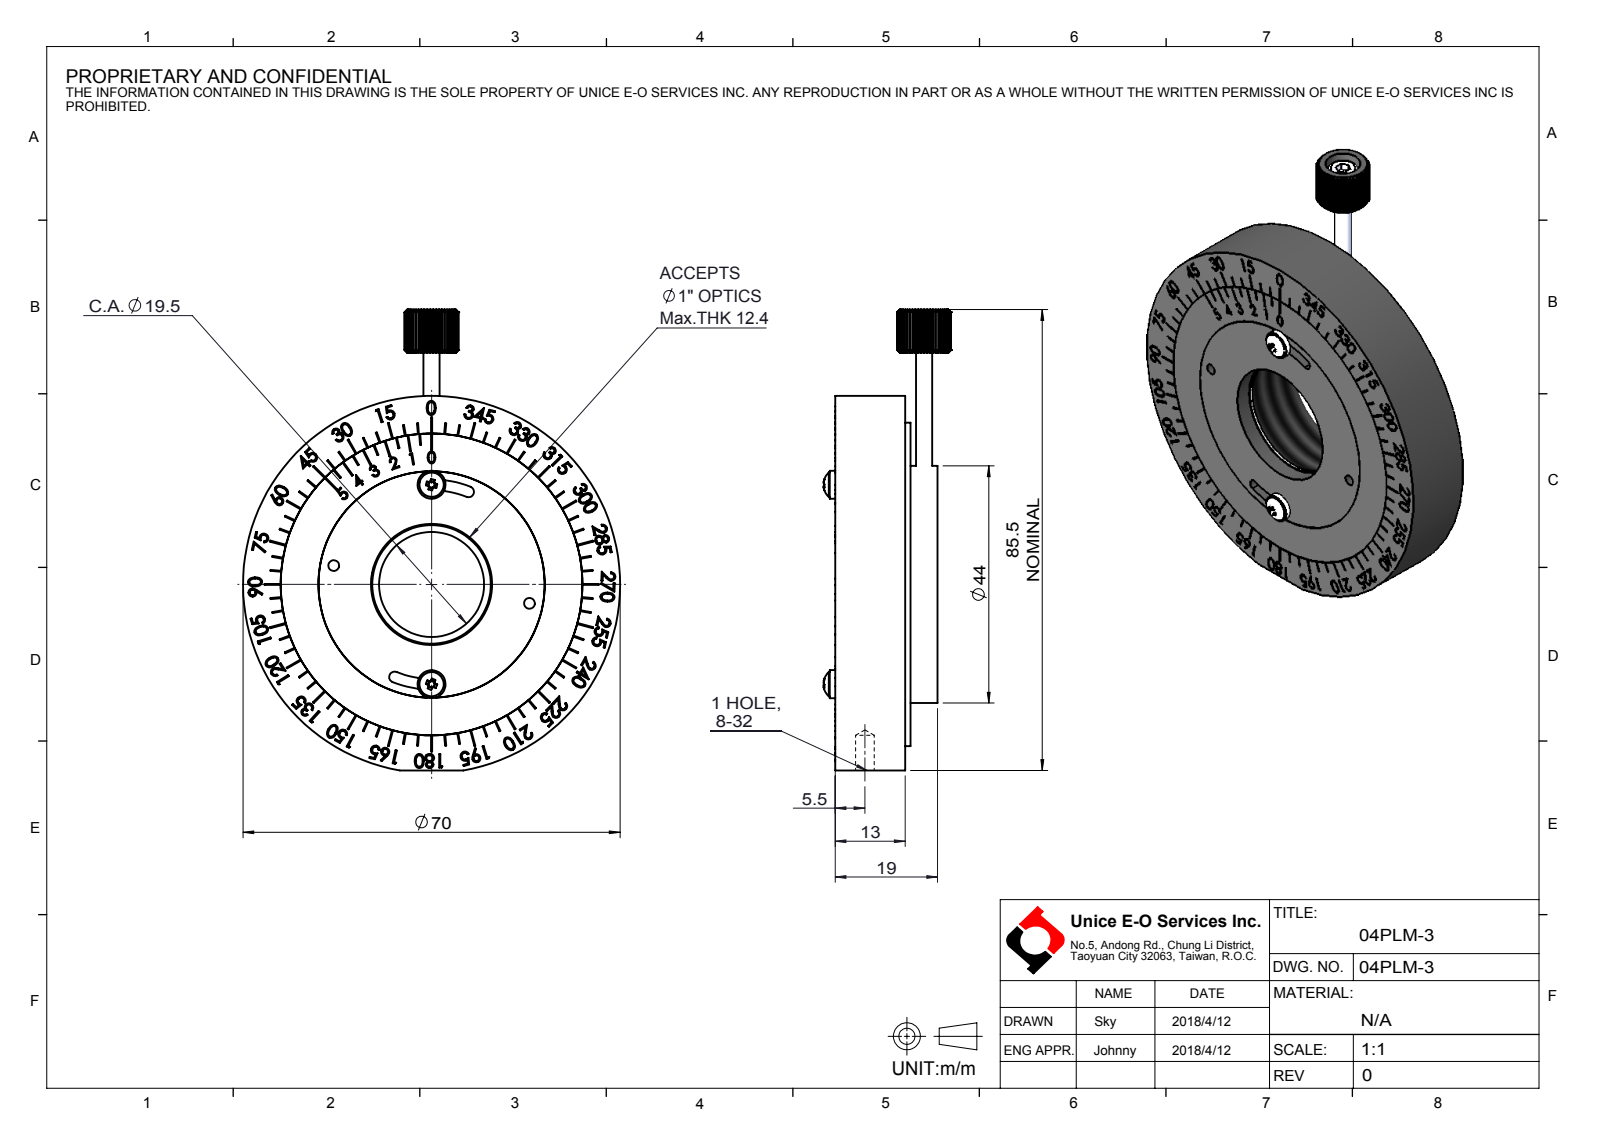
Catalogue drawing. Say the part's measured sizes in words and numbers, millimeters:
The part is named "04PLM-3". Its 3-D file was written by "SolidWorks 2016 (CONFIG_CONTROL_DESIGN)". It is 12 solids with 1590 faces: 915 planar, 144 cylindrical and 531 other. Overall it measures 85.5 by 70 by 23.64 millimeters. Its volume is 51 705 cubic millimeters and its surface area 30 242 square millimeters. Round holes: 5 of diameter 2, 2 of diameter 1.6, 2 of diameter 2.1, 1 of diameter 2.5, 1 of diameter 3.4, 1 of diameter 3.45, 1 of diameter 6.5, 1 of diameter 19.5, 1 of diameter 22, 1 of diameter 22.5, 1 of diameter 26.3, 1 of diameter 32. Round bosses or shafts: 2 of diameter 5.2, 2 of diameter 4.5, 1 of diameter 70, 1 of diameter 60, 1 of diameter 45.6, 1 of diameter 44, 1 of diameter 25, 1 of diameter 5.5. Partial cylindrical surfaces (rounded edges, fillets, slot ends): 2 of radius 1, 1 of radius 5, 1 of radius 17.5, 1 of radius 19.5. The main face-to-face distances are 5, 8, 3, 11, 6, 16, 14, 19, 13, 1. The hole center spacings are 18.5, 8.5, 23.56, 27, 28.53, 29.71, 35.5, 45.5.
